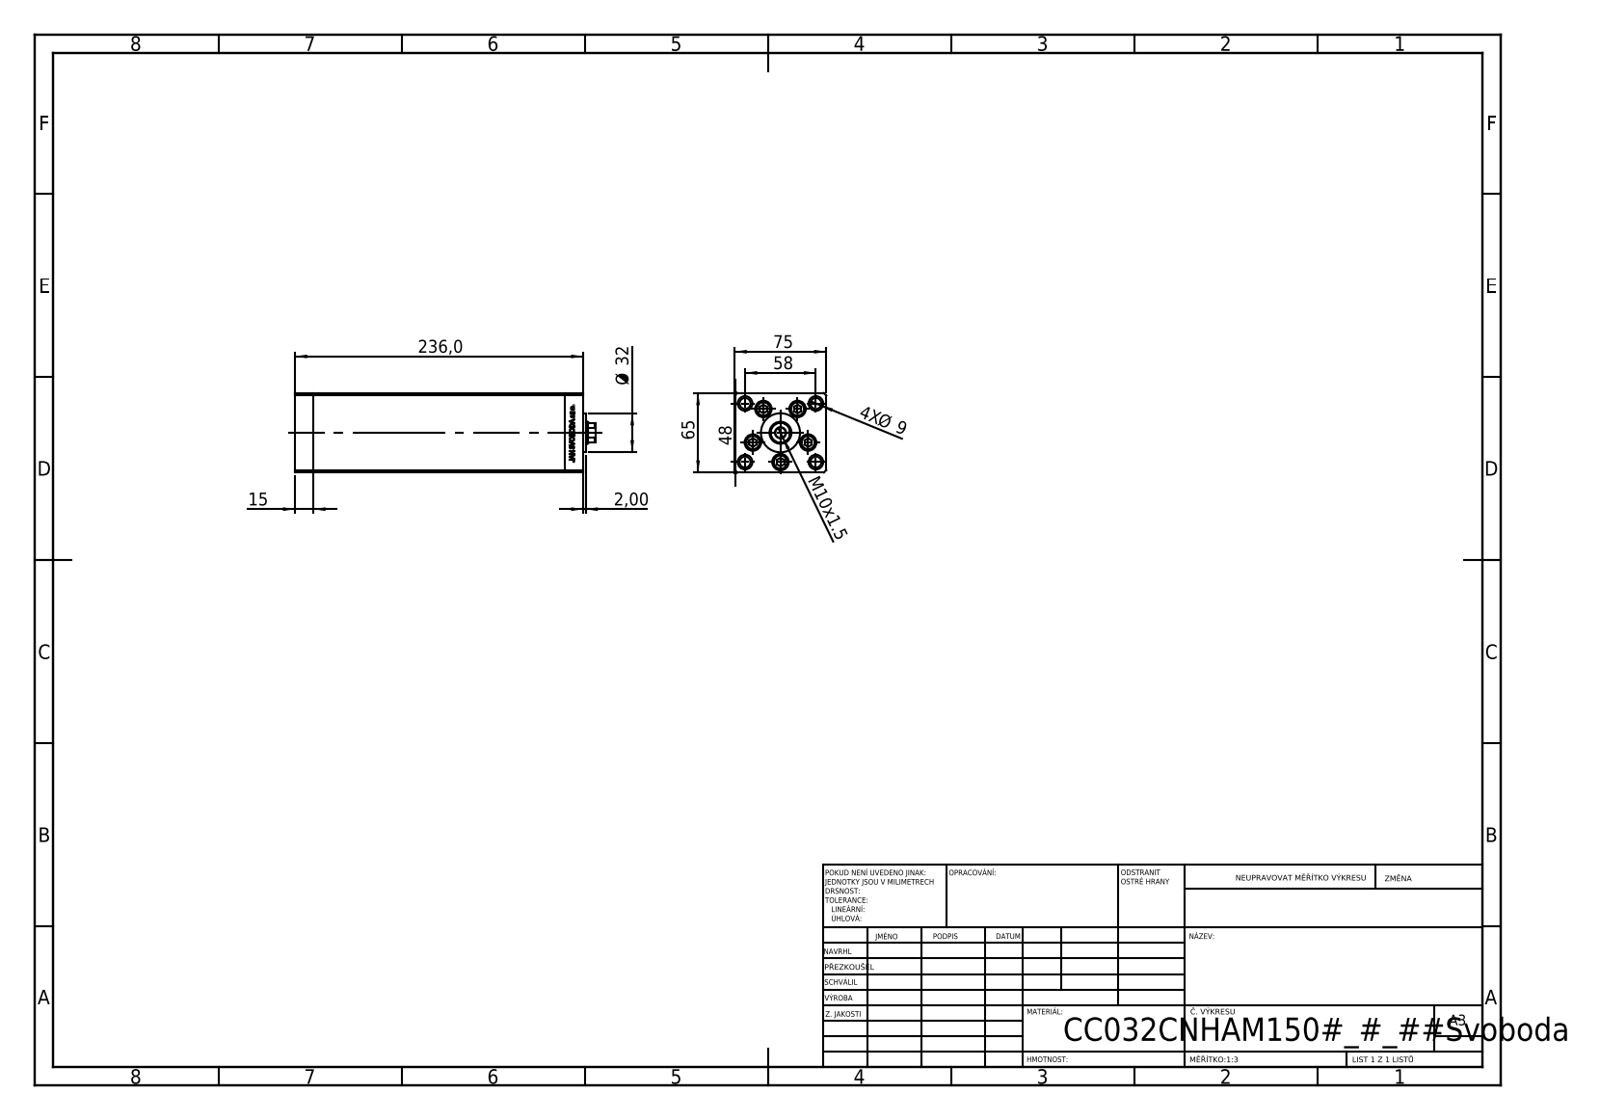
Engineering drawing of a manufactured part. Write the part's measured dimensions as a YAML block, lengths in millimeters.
part_name: "ALLEN BOLT; V220C_C MIDDLE; V220C_VC_C; V220C FRONT (+1 more)"
step_written_by: "SolidWorks 2019 (CONFIG_CONTROL_DESIGN)"
units: millimeters
bodies: {solids: 13, faces: 1183, planar: 546, cylindrical: 175, other: 462}
overall_size: [246, 75, 65]
volume: 958443
surface_area: 179366
round_holes:
  - {diameter: 9, count: 9}
  - {diameter: 13.5, count: 5}
  - {diameter: 2, count: 4}
  - {diameter: 8, count: 4}
  - {diameter: 12, count: 4}
  - {diameter: 13.16, count: 4}
  - {diameter: 8.5, count: 1}
  - {diameter: 12.5, count: 1}
  - {diameter: 18, count: 1}
round_bosses_or_shafts:
  - {diameter: 8, count: 5}
  - {diameter: 12.5, count: 4}
  - {diameter: 32, count: 1}
partial_cylinders:
  - {radius: 0.93, count: 2}
  - {radius: 8.5, count: 1}
face_to_face_distances: [75, 65, 15, 206, 221, 236, 54.5, 10.5, 26.25, 48.75]
hole_center_spacings: [24, 37.64, 15.67, 17.22, 27.71, 28.83, 29, 32.63]
